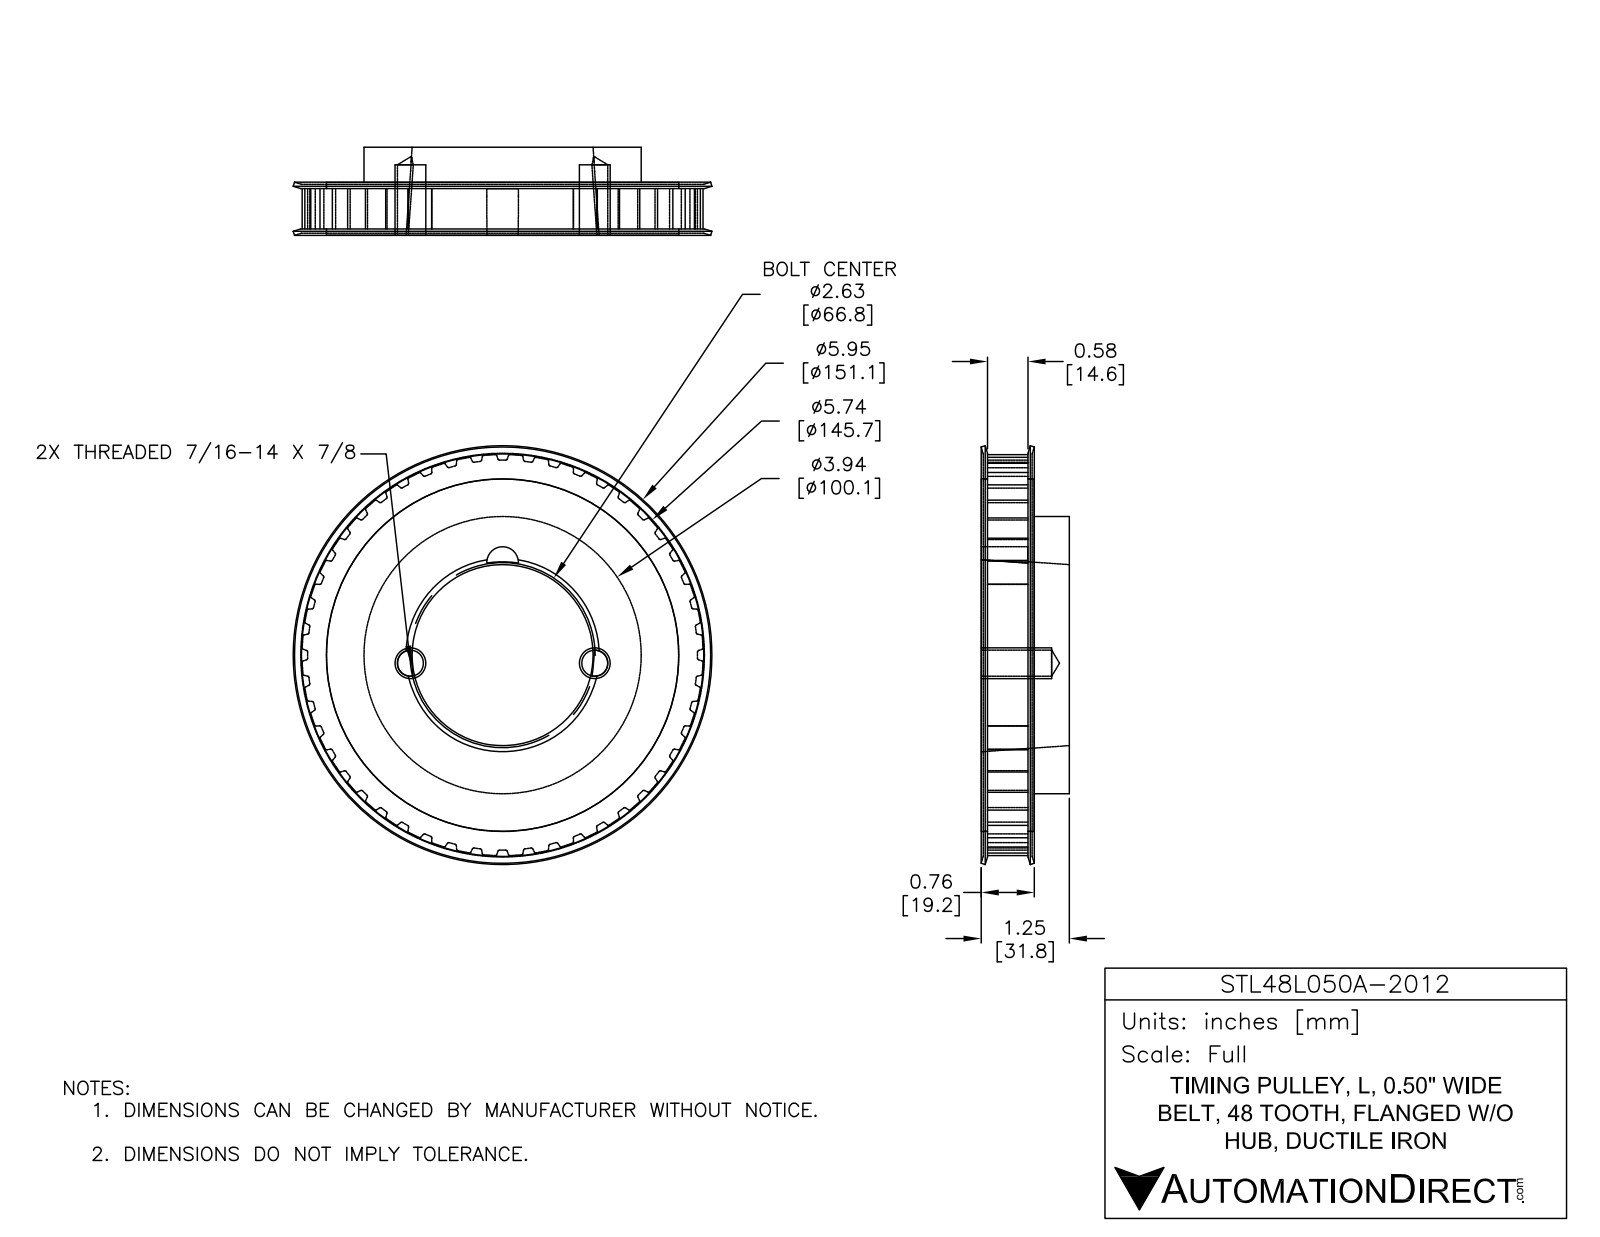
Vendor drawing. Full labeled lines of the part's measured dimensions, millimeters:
Part name (STEP PRODUCT): STL48L050AF-2012
STEP written by: SolidWorks 2018 (AUTOMOTIVE_DESIGN)
Units: millimetres
Bodies: 4 solids, 466 faces (154 planar, 294 cylindrical, 18 other)
Overall size (bounding box): 151.13 × 151.13 × 31.81
Volume: 291 277 mm³ · Surface area: 81 432 mm²
Round holes (diameter × count): ⌀127.1 ×1, ⌀127.23 ×1
Round bosses / shafts (diameter × count): ⌀100.08 ×1
Partial cylindrical surfaces — rounded edges, fillets, slot ends (radius × count): R0.38 ×96, R0.51 ×96, R4.7 ×2, R5.71 ×1, R72.39 ×1
Main face-to-face distances: 16.83, 2.22, 0.7, 18.35, 1.52, 16.13, 14.61, 19.05, 12.7, 14.92
